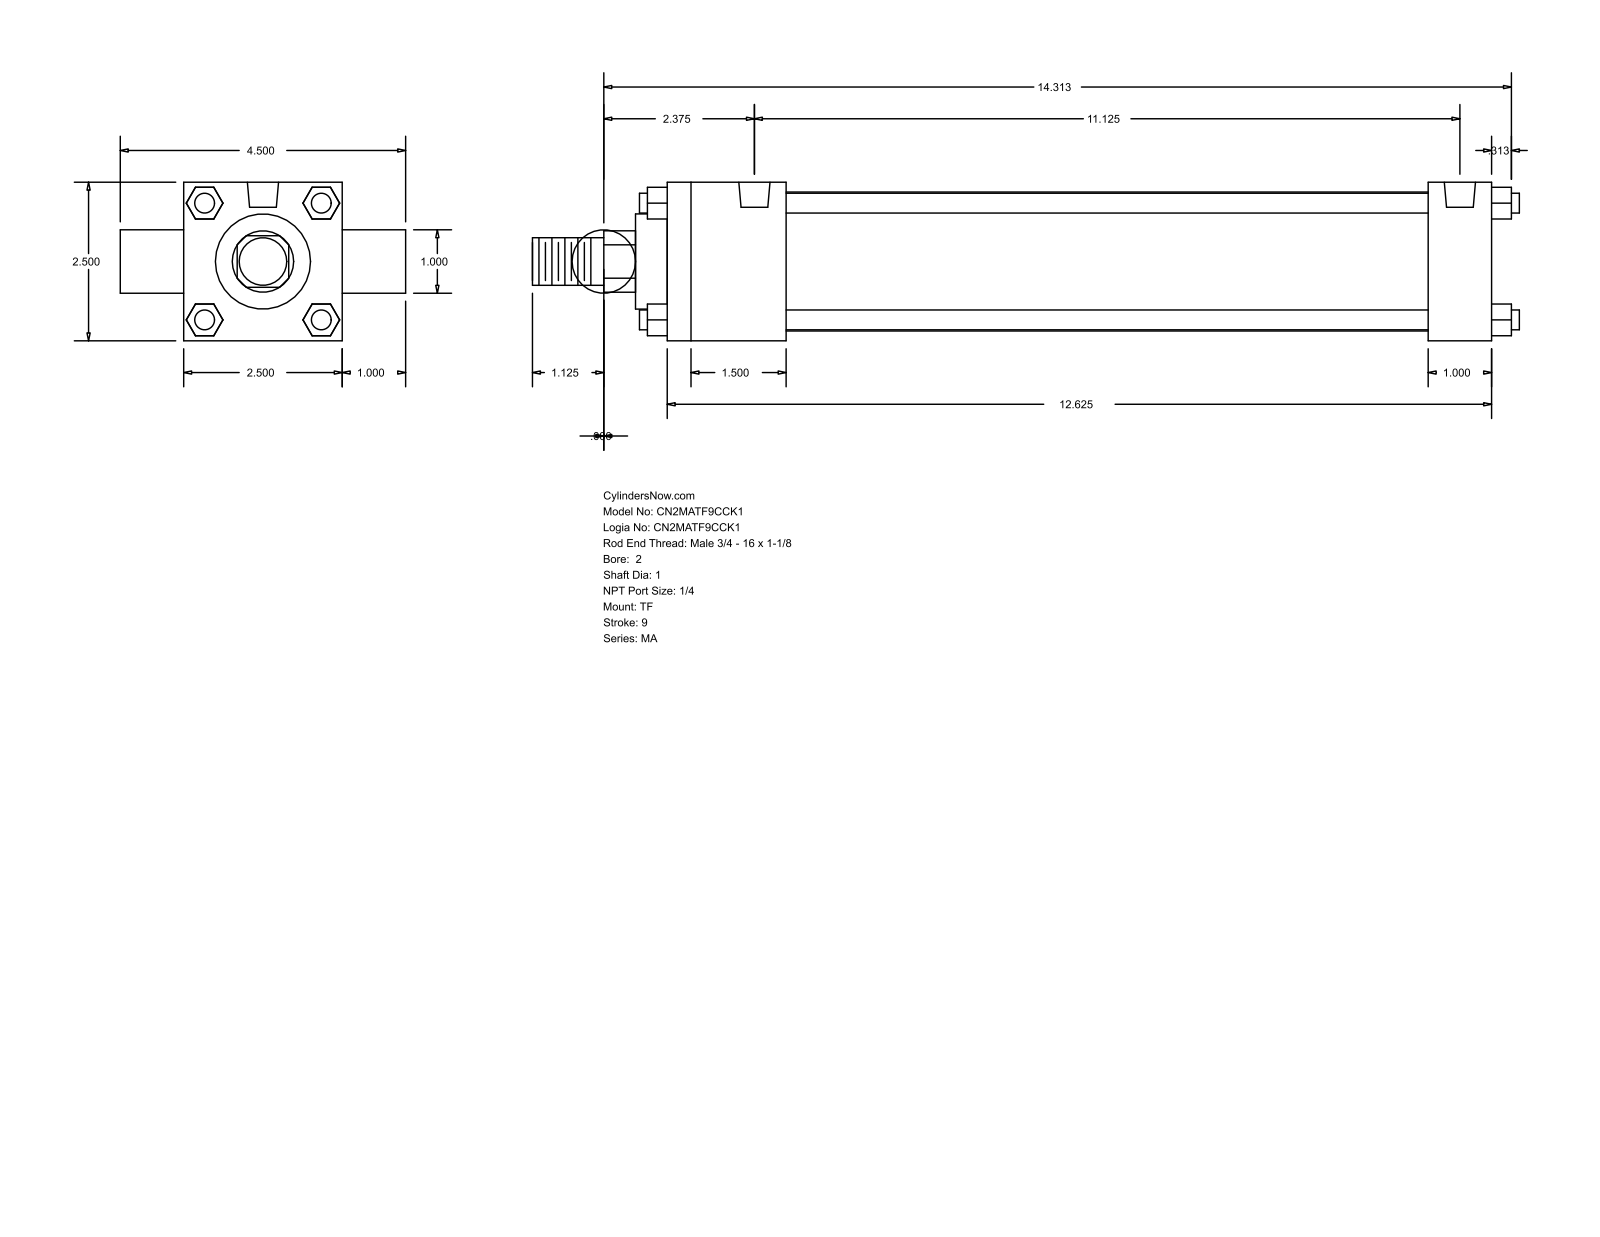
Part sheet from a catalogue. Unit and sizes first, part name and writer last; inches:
Units: inches
Overall size (bounding box): 15.563 × 4.5 × 2.5
Round holes (diameter × count): ⌀0.313 ×3, ⌀0.492 ×2
Round bosses / shafts (diameter × count): ⌀0.313 ×4, ⌀1 ×2, ⌀2.19 ×1, ⌀1.5 ×1, ⌀0.75 ×1
Partial cylindrical surfaces — rounded edges, fillets, slot ends (radius × count): R0.484 ×1
Main face-to-face distances: 2.5, 1, 13, 0.5, 1.875, 12, 10.125, 11.125, 3.5, 1.593
Hole centre spacings: 11.125
Bodies: 0 solids, 120 faces (92 planar, 28 cylindrical, 0 other)
Part name (STEP PRODUCT): MA_TF__0200_1
STEP written by: GSSL Pune (CONFIG_CONTROL_DESIGN)
